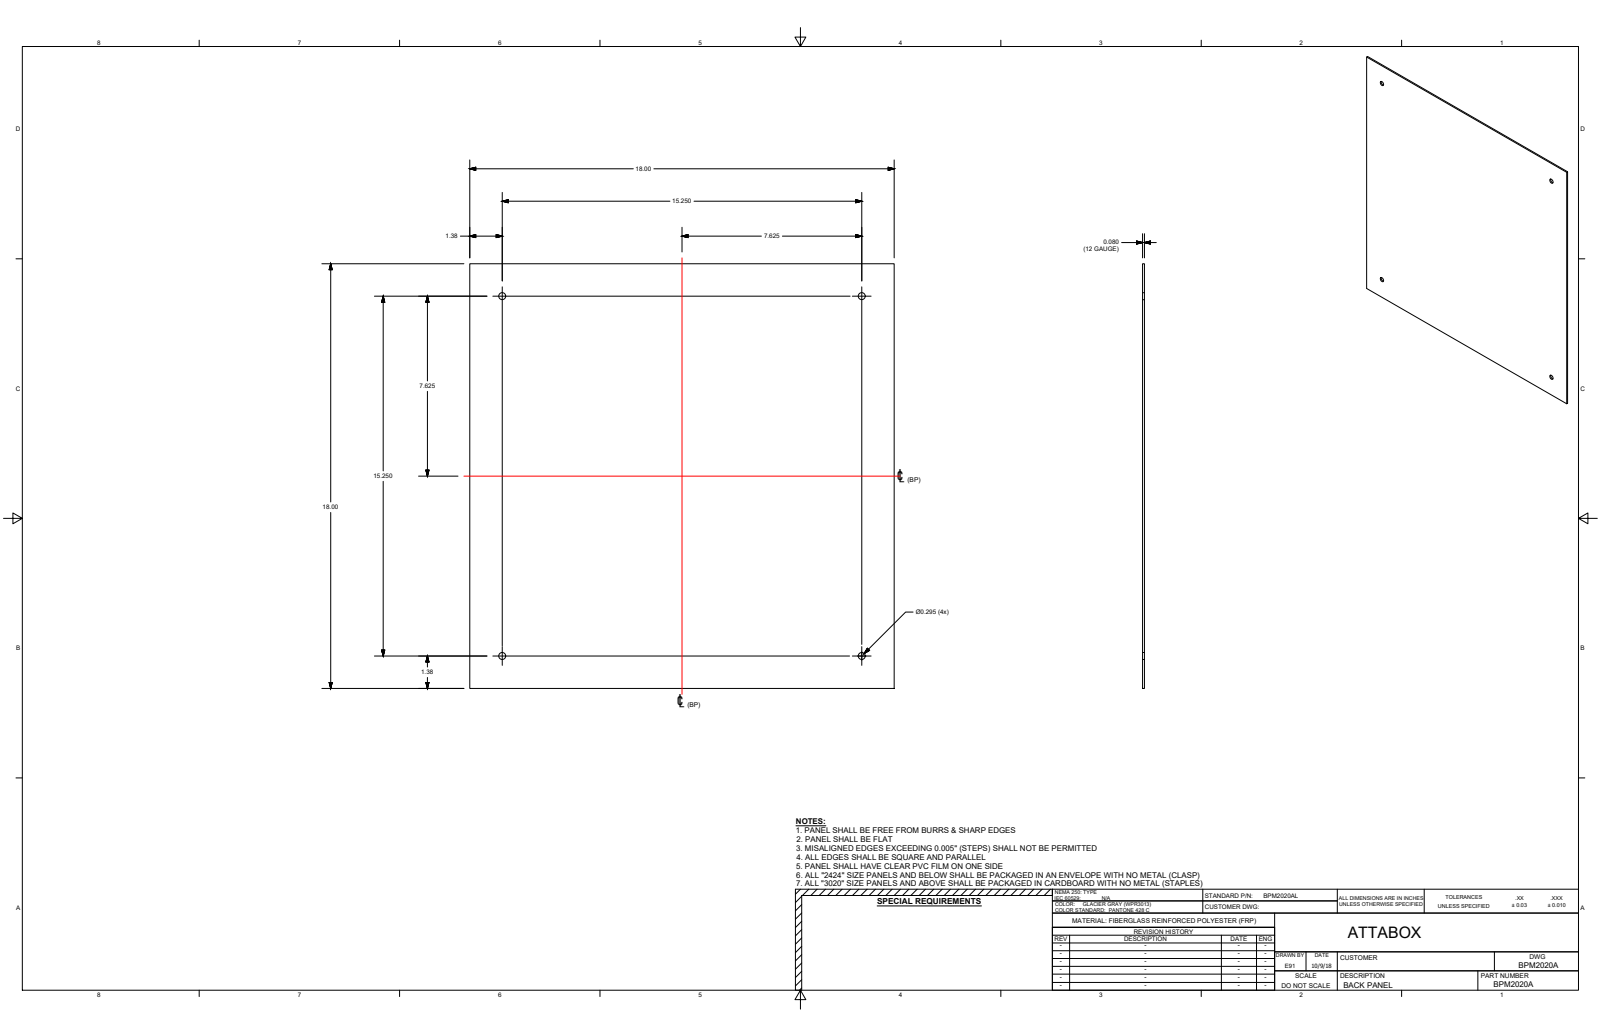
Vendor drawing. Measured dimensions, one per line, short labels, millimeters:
name: HW-MP2020AL
written by: Autodesk Inventor 2017 (CONFIG_CONTROL_DESIGN)
unit: mm
bodies: 1 solid, 10 faces (6 planar, 4 cylindrical, 0 other)
size: 457.2 × 457.2 × 2.03
volume: 424 394 mm³; area: 421 618 mm²
holes: 4× ⌀7.49
face distances: 2.03, 457.2
hole spacings: 387.35, 547.8
